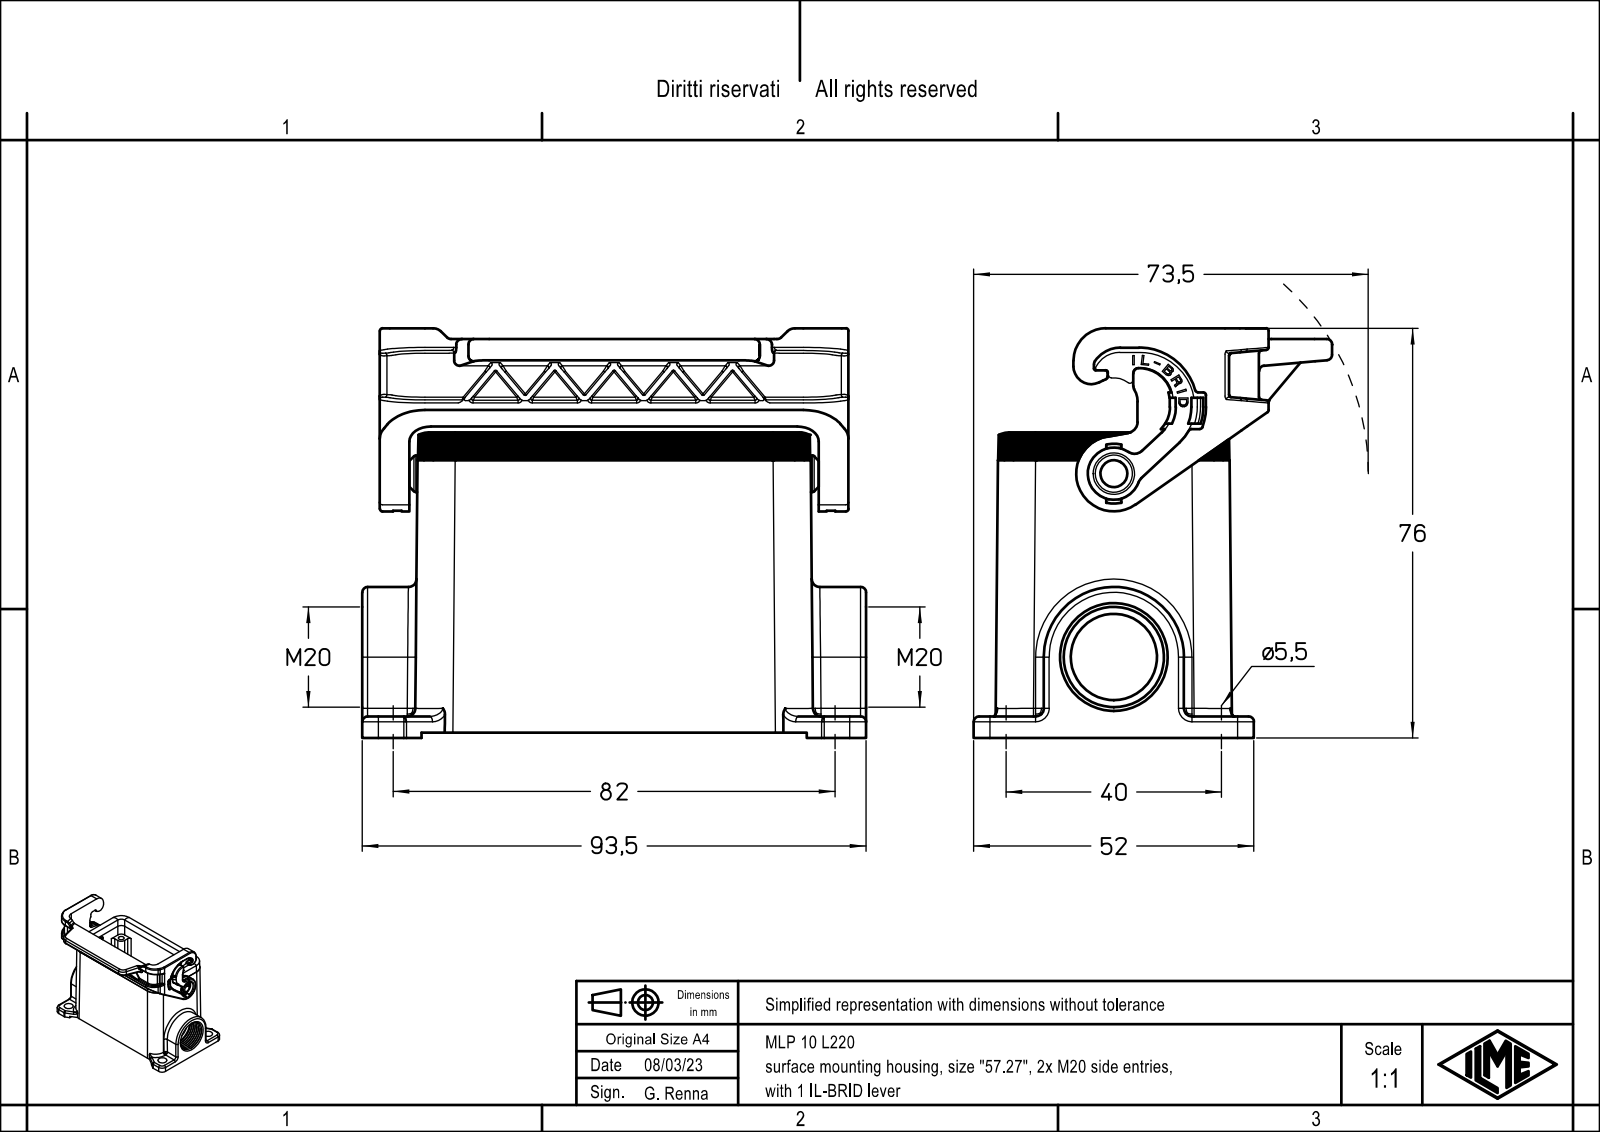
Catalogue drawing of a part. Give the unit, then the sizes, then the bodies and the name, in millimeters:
Units: millimetres
Overall size (bounding box): 93.5 × 76 × 66.5
Round holes (diameter × count): ⌀3 ×4, ⌀3.5 ×4, ⌀5 ×4, ⌀5.5 ×4, ⌀3.25 ×1, ⌀5.4 ×1, ⌀7.7 ×1, ⌀16 ×1, ⌀18.6 ×1
Round bosses / shafts (diameter × count): ⌀6.9 ×1, ⌀6.8 ×1, ⌀5.2 ×1, ⌀3.2 ×1
Partial cylindrical surfaces — rounded edges, fillets, slot ends (radius × count): R0.1 ×27, R1 ×18, R1.5 ×17, R2 ×17, R3 ×16, R0.2 ×15, R0.5 ×11, R7 ×10
Main face-to-face distances: 3, 1, 76, 4, 5.5, 81.5, 74, 73, 70, 38.95
Hole centre spacings: 2.92, 11.7, 14.09, 29.54, 35.76, 37.64, 58.55, 65.52
Volume: 88 390 mm³ · Surface area: 46 826 mm²
Bodies: 1 solid, 1087 faces (621 planar, 306 cylindrical, 160 other)
Part name (STEP PRODUCT): MLP 10 L220
STEP written by: Creo Elements/Direct Modeling 20.1B 02-Apr-2019 (C) Parametric Technology GmbH (AUTOMOTIVE_DESIGN)
